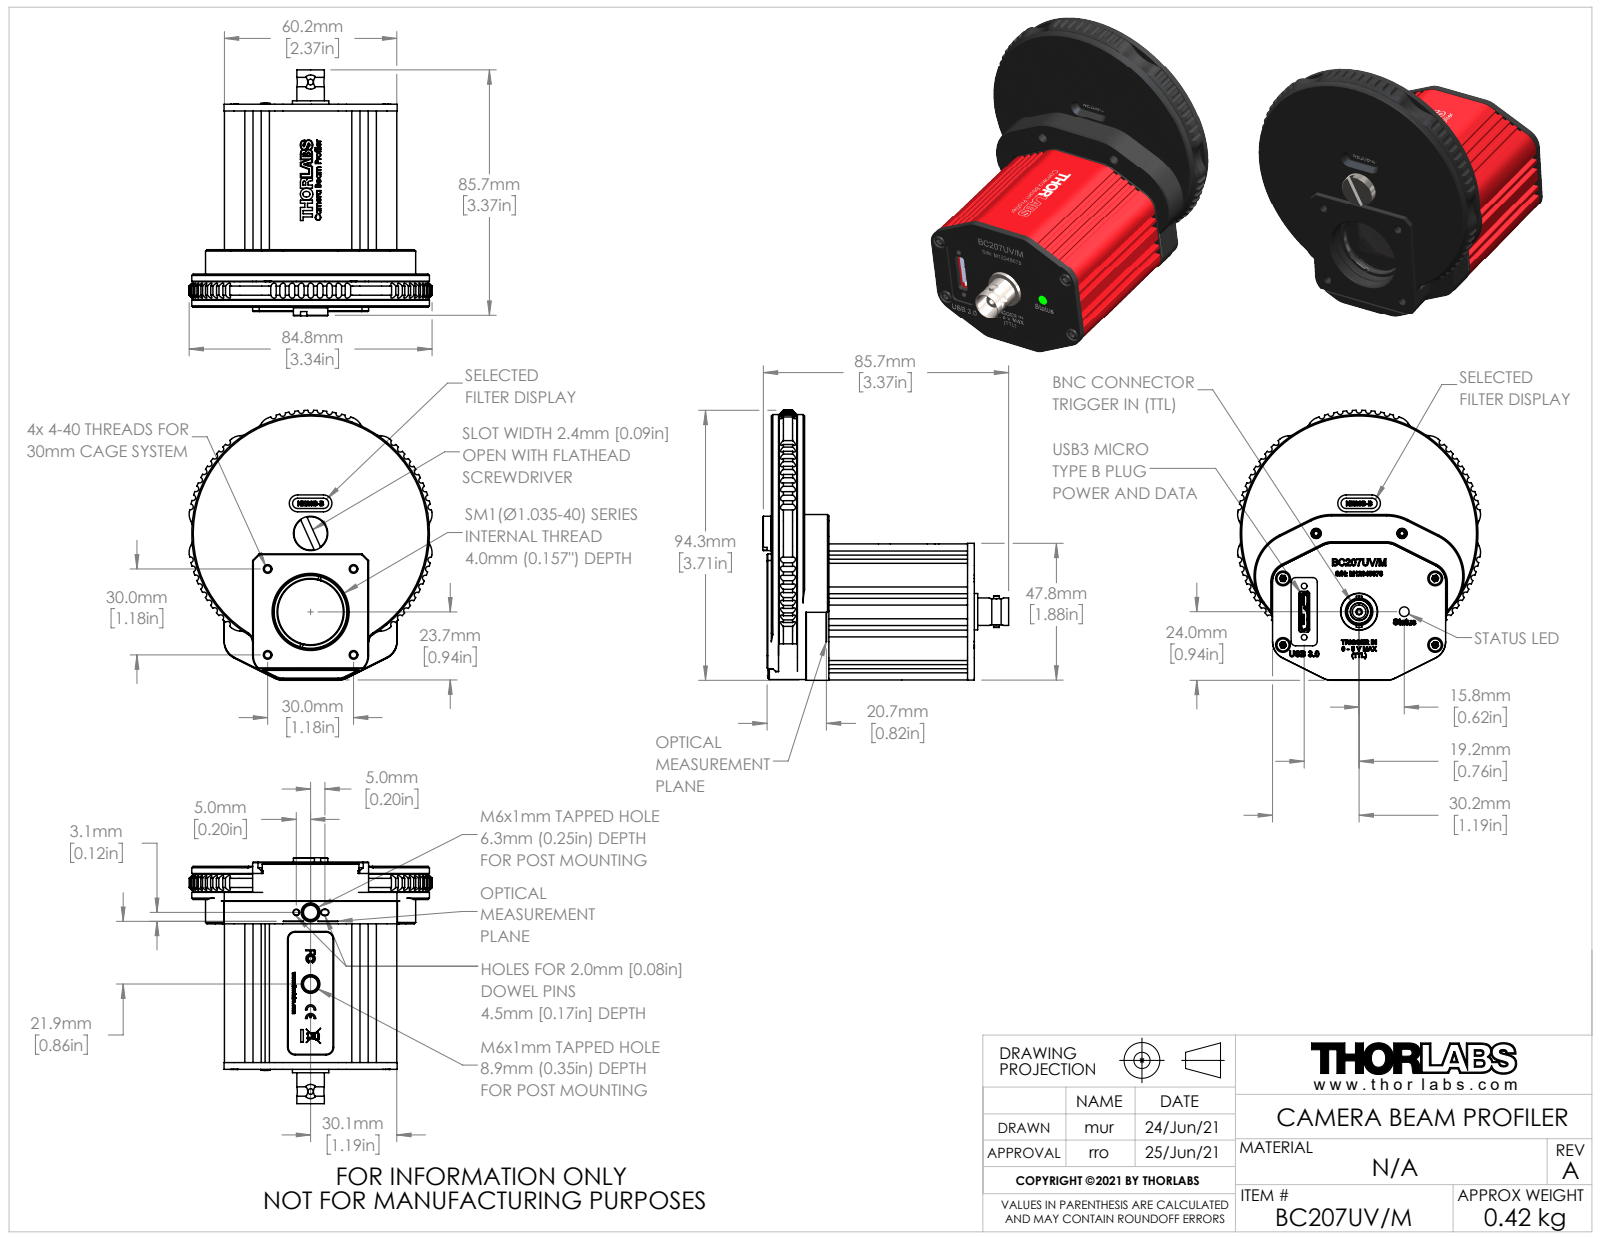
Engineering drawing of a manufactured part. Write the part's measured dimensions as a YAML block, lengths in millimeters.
part_name: "21.08.18_BC207UV_M_WEB"
step_written_by: "SolidWorks 2019 (AUTOMOTIVE_DESIGN)"
units: millimeters
bodies: {solids: 58, faces: 6126, planar: 3340, cylindrical: 1208, other: 1578}
overall_size: [94.27, 85.86, 84.85]
volume: 143591
surface_area: 106841
round_holes:
  - {diameter: 2.26, count: 12}
  - {diameter: 5.16, count: 8}
  - {diameter: 25.96, count: 7}
  - {diameter: 0.8, count: 6}
  - {diameter: 22.91, count: 6}
  - {diameter: 23, count: 6}
  - {diameter: 25.5, count: 6}
  - {diameter: 26.5, count: 6}
  - {diameter: 1.6, count: 5}
  - {diameter: 1.78, count: 5}
  - {diameter: 2.18, count: 5}
  - {diameter: 2, count: 4}
round_bosses_or_shafts:
  - {diameter: 0.69, count: 226}
  - {diameter: 4.24, count: 8}
  - {diameter: 26.29, count: 7}
  - {diameter: 25, count: 7}
  - {diameter: 5.9, count: 4}
  - {diameter: 1.02, count: 4}
  - {diameter: 5.08, count: 2}
  - {diameter: 4.7, count: 2}
partial_cylinders:
  - {radius: 0.2, count: 79}
  - {radius: 0.1, count: 56}
  - {radius: 1, count: 56}
  - {radius: 0.14, count: 48}
  - {radius: 0.81, count: 48}
  - {radius: 6.35, count: 36}
  - {radius: 0.5, count: 28}
  - {radius: 0.81, count: 24}
face_to_face_distances: [2.5, 9.1, 6.6, 8.5, 6.4, 9.6, 8.9, 2.7, 3, 12.1]
hole_center_spacings: [53.16, 29, 41.72, 28.97, 30, 12.07, 12.09, 14.7]
